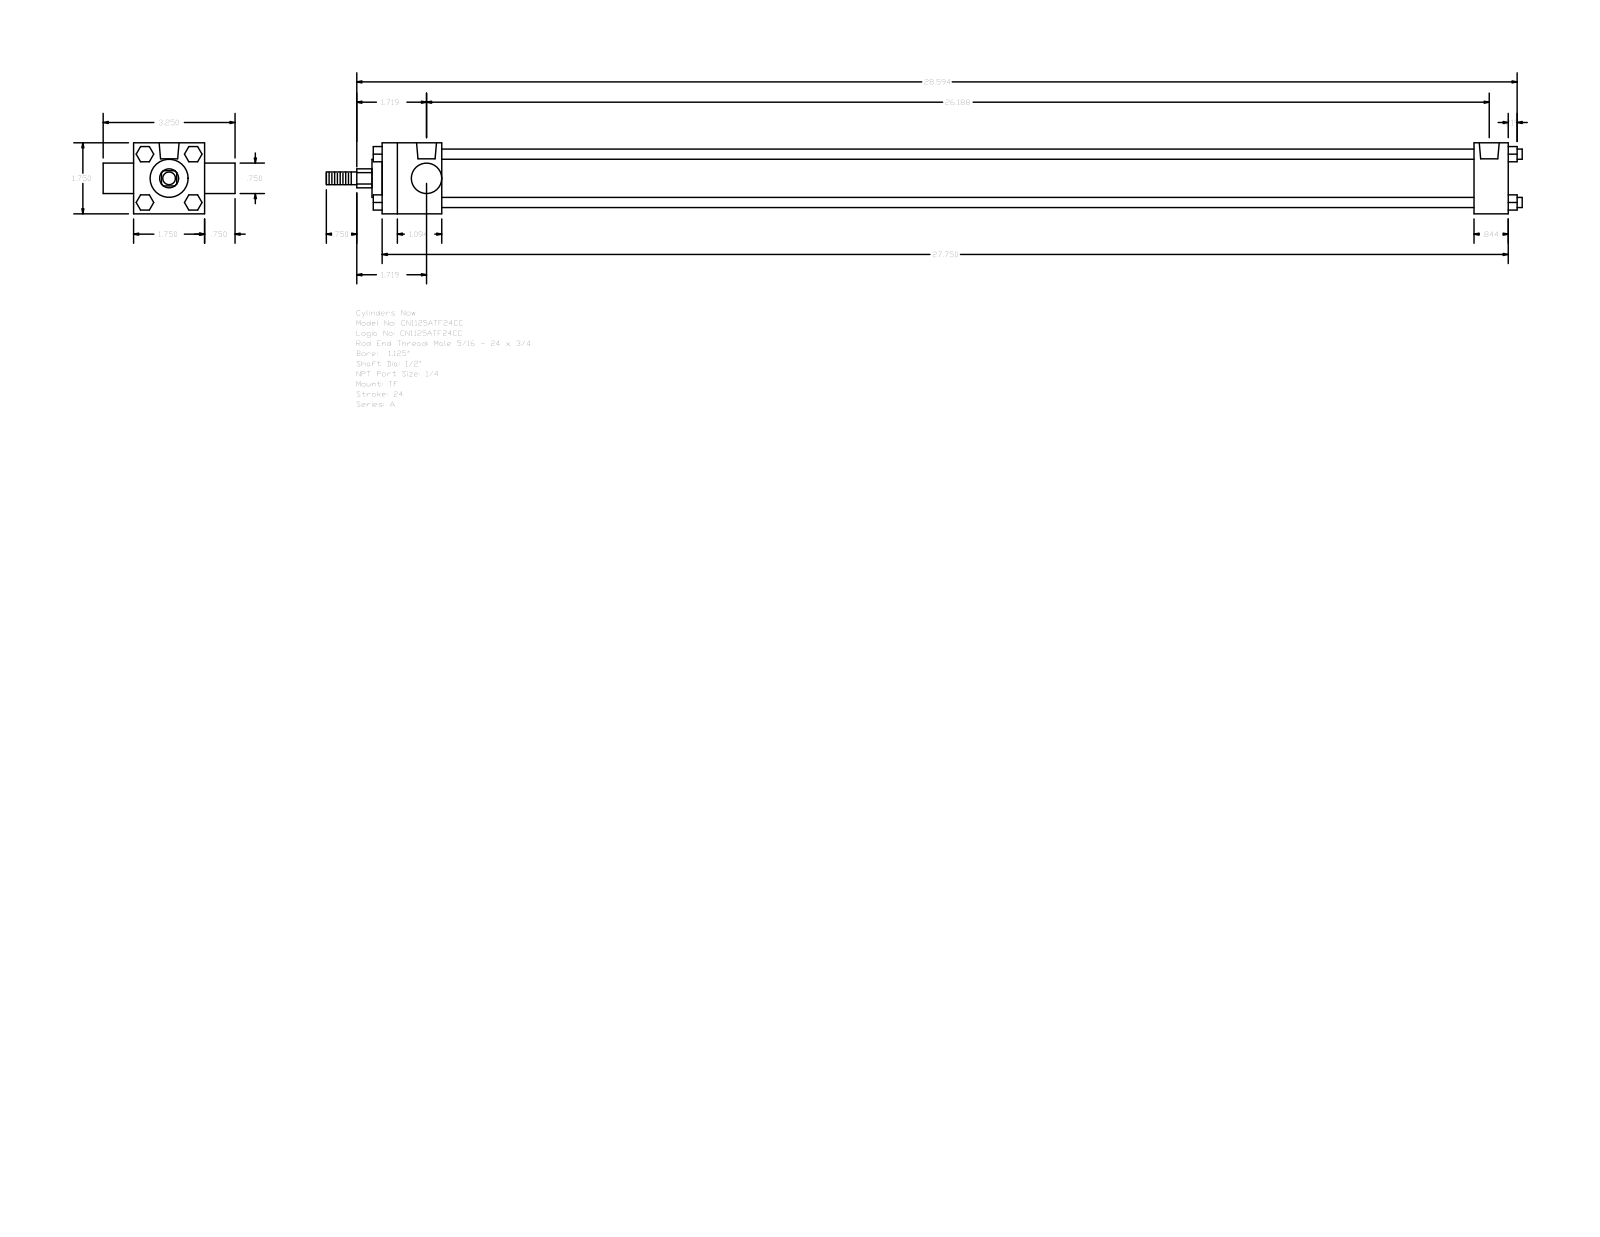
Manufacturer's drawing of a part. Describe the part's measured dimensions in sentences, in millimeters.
The part is named "A_TF__0112_0.5". Its 3-D file was written by "GSSL Pune (CONFIG_CONTROL_DESIGN)". It is 0 solids with 120 faces: 92 planar, 28 cylindrical and 0 other. Overall it measures 748.51 by 82.55 by 44.45 millimeters. Round holes: 3 of diameter 5.56, 2 of diameter 12.49. Round bosses or shafts: 4 of diameter 6.35, 1 of diameter 31.88, 1 of diameter 23.81, 1 of diameter 19.05, 1 of diameter 12.7, 1 of diameter 7.94. Partial cylindrical surfaces (rounded edges, fillets, slot ends): 1 of radius 5.94. The main face-to-face distances are 44.46, 704.85, 683.41, 21.44, 37.3, 646.11, 667.55, 19.04, 63.5, 9.53. The hole center spacings are 1.58, 1.59, 661.99, 663.57, 663.58, 665.16.
